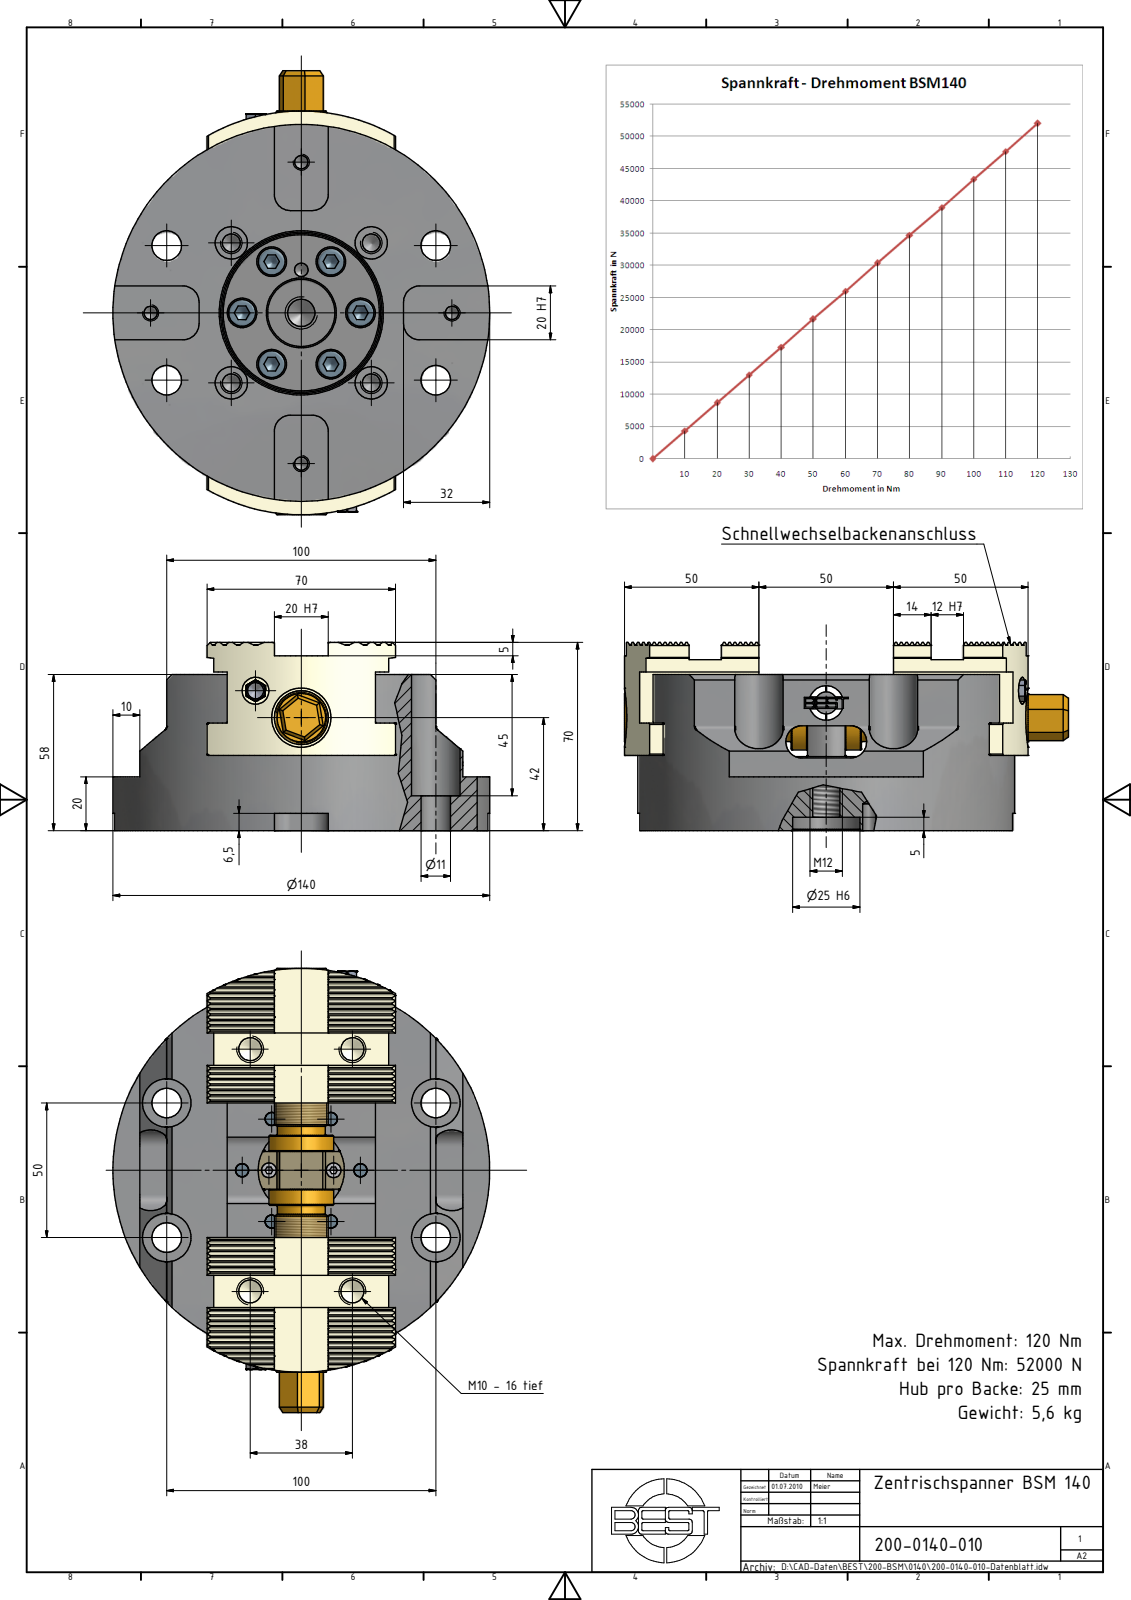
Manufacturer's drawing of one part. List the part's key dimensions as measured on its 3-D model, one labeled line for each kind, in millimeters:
Part name (STEP PRODUCT): 200-0140-010-Kunde
STEP written by: Autodesk Inventor 2013 (AUTOMOTIVE_DESIGN)
Units: millimetres
Bodies: 1 solid, 691 faces (453 planar, 151 cylindrical, 87 other)
Overall size (bounding box): 170.8 × 140 × 82
Volume: 750 922 mm³ · Surface area: 107 145 mm²
Round holes (diameter × count): ⌀4.92 ×8, ⌀6.65 ×4, ⌀8.5 ×4, ⌀11 ×4, ⌀12 ×4, ⌀18 ×4, ⌀5 ×2, ⌀10 ×2, ⌀10.11 ×1, ⌀25 ×1, ⌀32 ×1, ⌀60 ×1
Round bosses / shafts (diameter × count): ⌀16 ×4, ⌀10 ×4, ⌀3 ×2, ⌀140 ×1, ⌀59 ×1, ⌀24 ×1, ⌀20 ×1
Partial cylindrical surfaces — rounded edges, fillets, slot ends (radius × count): R0.2 ×18, R0.51 ×12, R8 ×8, R0.4 ×4, R0.64 ×4, R1.15 ×4, R2 ×2, R6 ×2
Main face-to-face distances: 12, 58, 70, 50, 25, 20, 30, 22.5, 5, 1
Hole centre spacings: 71.84, 86.02, 32.2, 39.7, 48.85, 75.61, 11, 19
